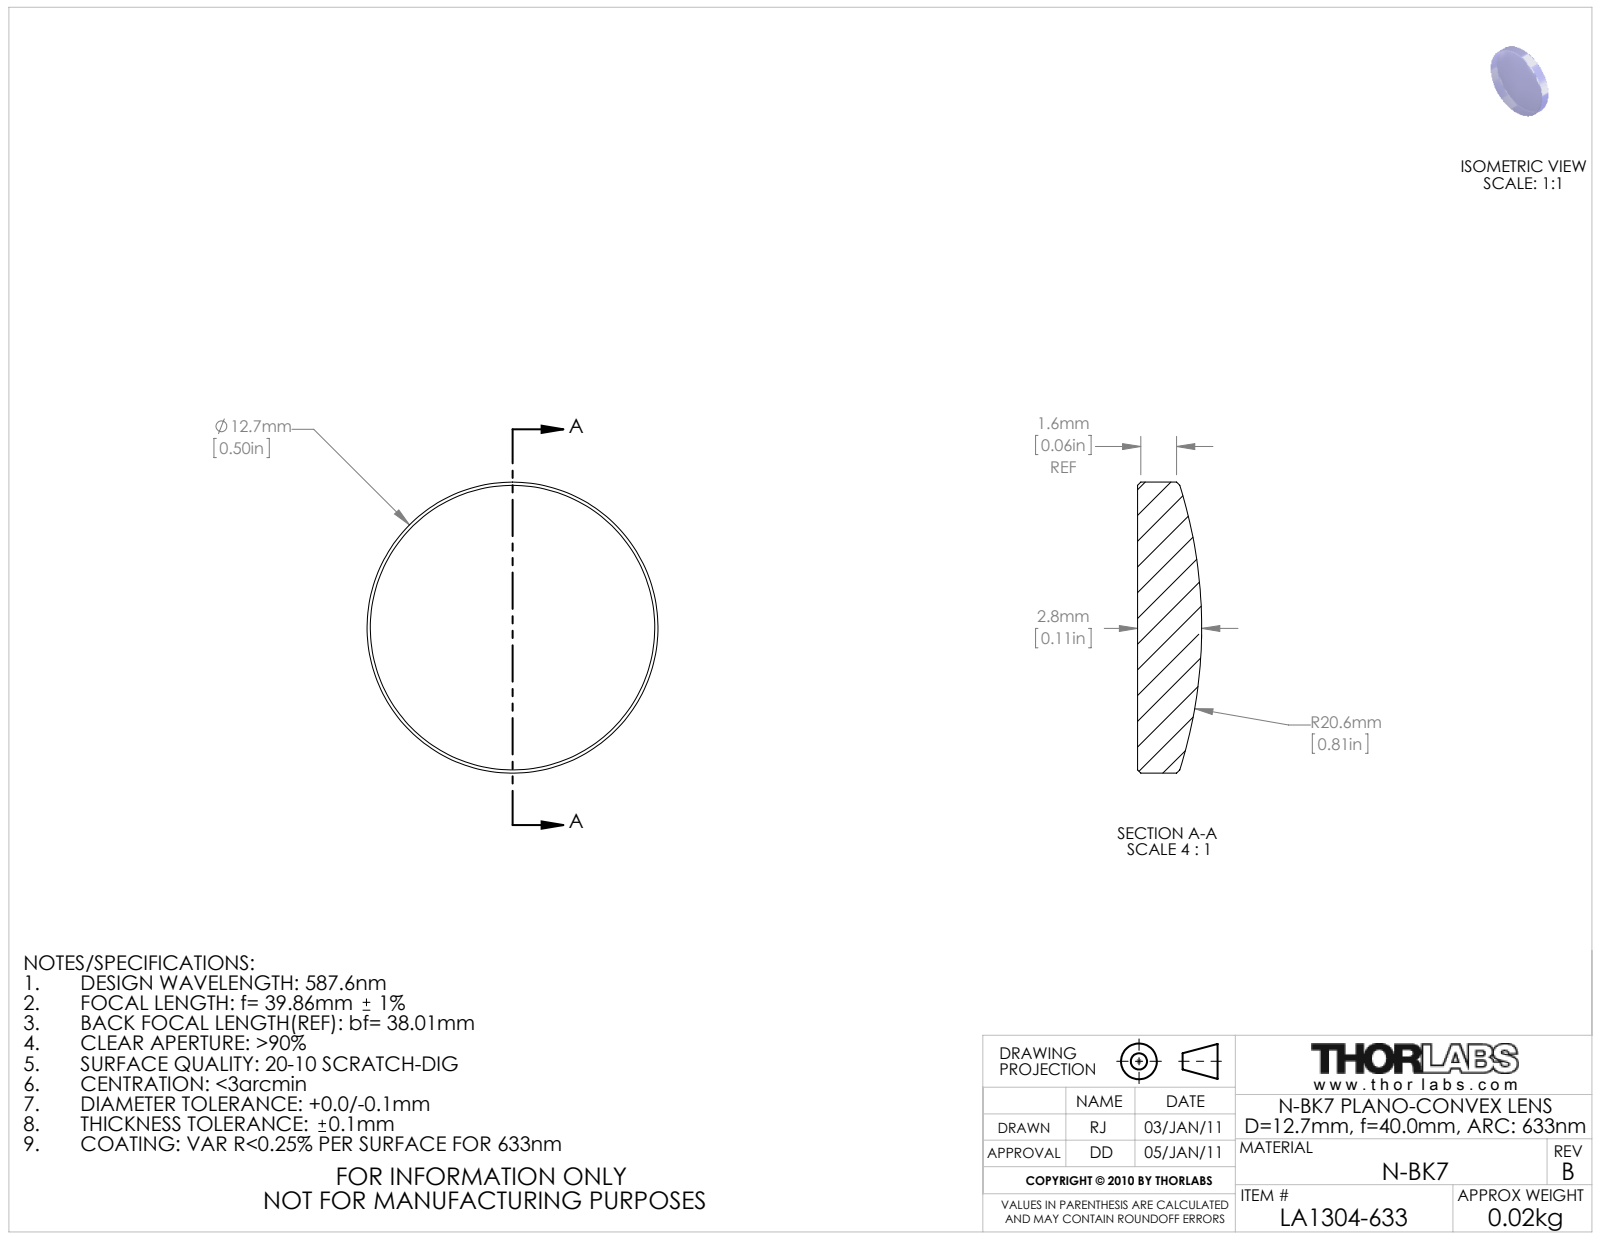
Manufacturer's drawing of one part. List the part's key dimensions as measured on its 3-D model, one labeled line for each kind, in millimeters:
Part name (STEP PRODUCT): 21780-E0W
STEP written by: SolidWorks 2011 (AUTOMOTIVE_DESIGN)
Units: millimetres
Bodies: 0 solids, 9 faces (1 planar, 2 cylindrical, 6 other)
Overall size (bounding box): 12.7 × 12.7 × 2.8
Round bosses / shafts (diameter × count): ⌀12.7 ×1
